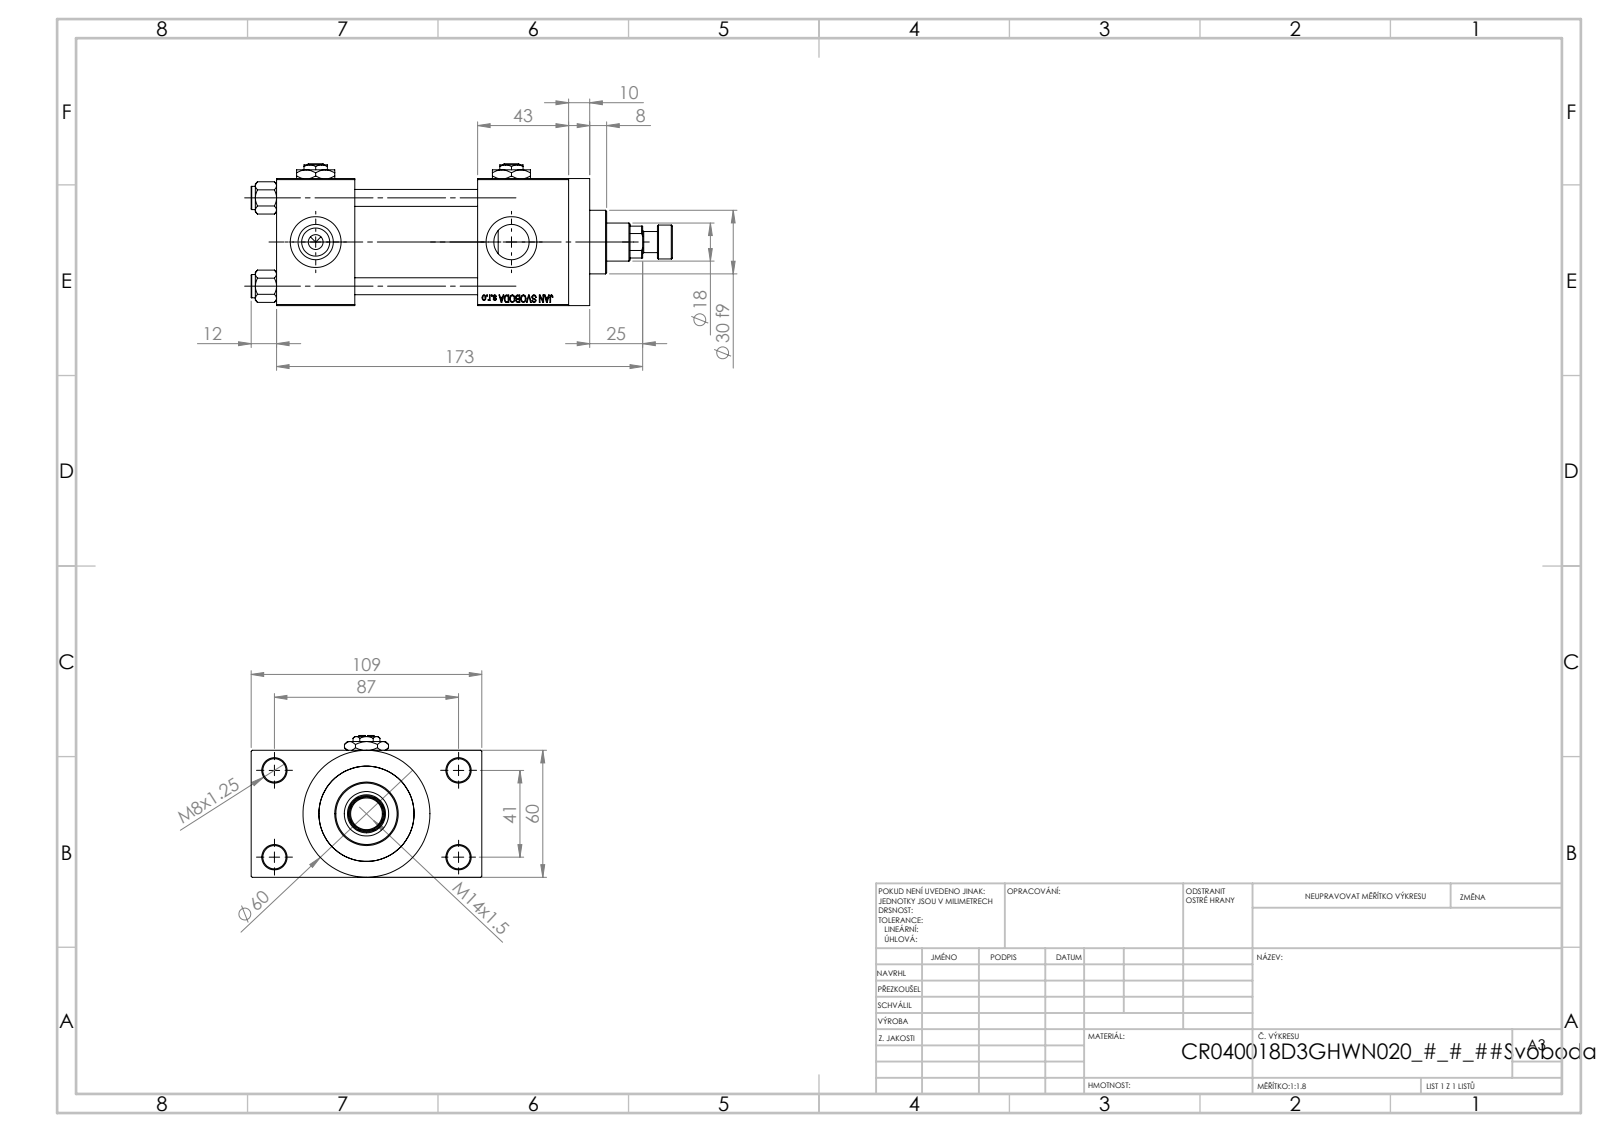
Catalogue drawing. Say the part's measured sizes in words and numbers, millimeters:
The part is named "V215CR_D_TYCINKA; NUT_M5_D; V215CR_VCP_D; V215CR_ROD_END_W (+3 more)". Its 3-D file was written by "SolidWorks 2019 (CONFIG_CONTROL_DESIGN)". It is 14 solids with 1218 faces: 549 planar, 103 cylindrical and 566 other. Overall it measures 199 by 109 by 67 millimeters. Its volume is 512 293 cubic millimeters and its surface area 126 168 square millimeters. Round holes: 4 of diameter 8, 4 of diameter 11, 4 of diameter 16.66, 4 of diameter 24, 3 of diameter 7, 1 of diameter 8.5, 1 of diameter 18, 1 of diameter 21, 1 of diameter 31, 1 of diameter 40, 1 of diameter 45. Round bosses or shafts: 4 of diameter 11, 1 of diameter 60, 1 of diameter 46, 1 of diameter 30, 1 of diameter 16, 1 of diameter 10. Partial cylindrical surfaces (rounded edges, fillets, slot ends): 1 of radius 8.5. The main face-to-face distances are 60, 24.5, 58, 84.5, 37, 95, 43, 138, 101, 10. The hole center spacings are 22.65, 29.49, 41.7, 47.15, 48.09, 64.35, 76.49, 41.
